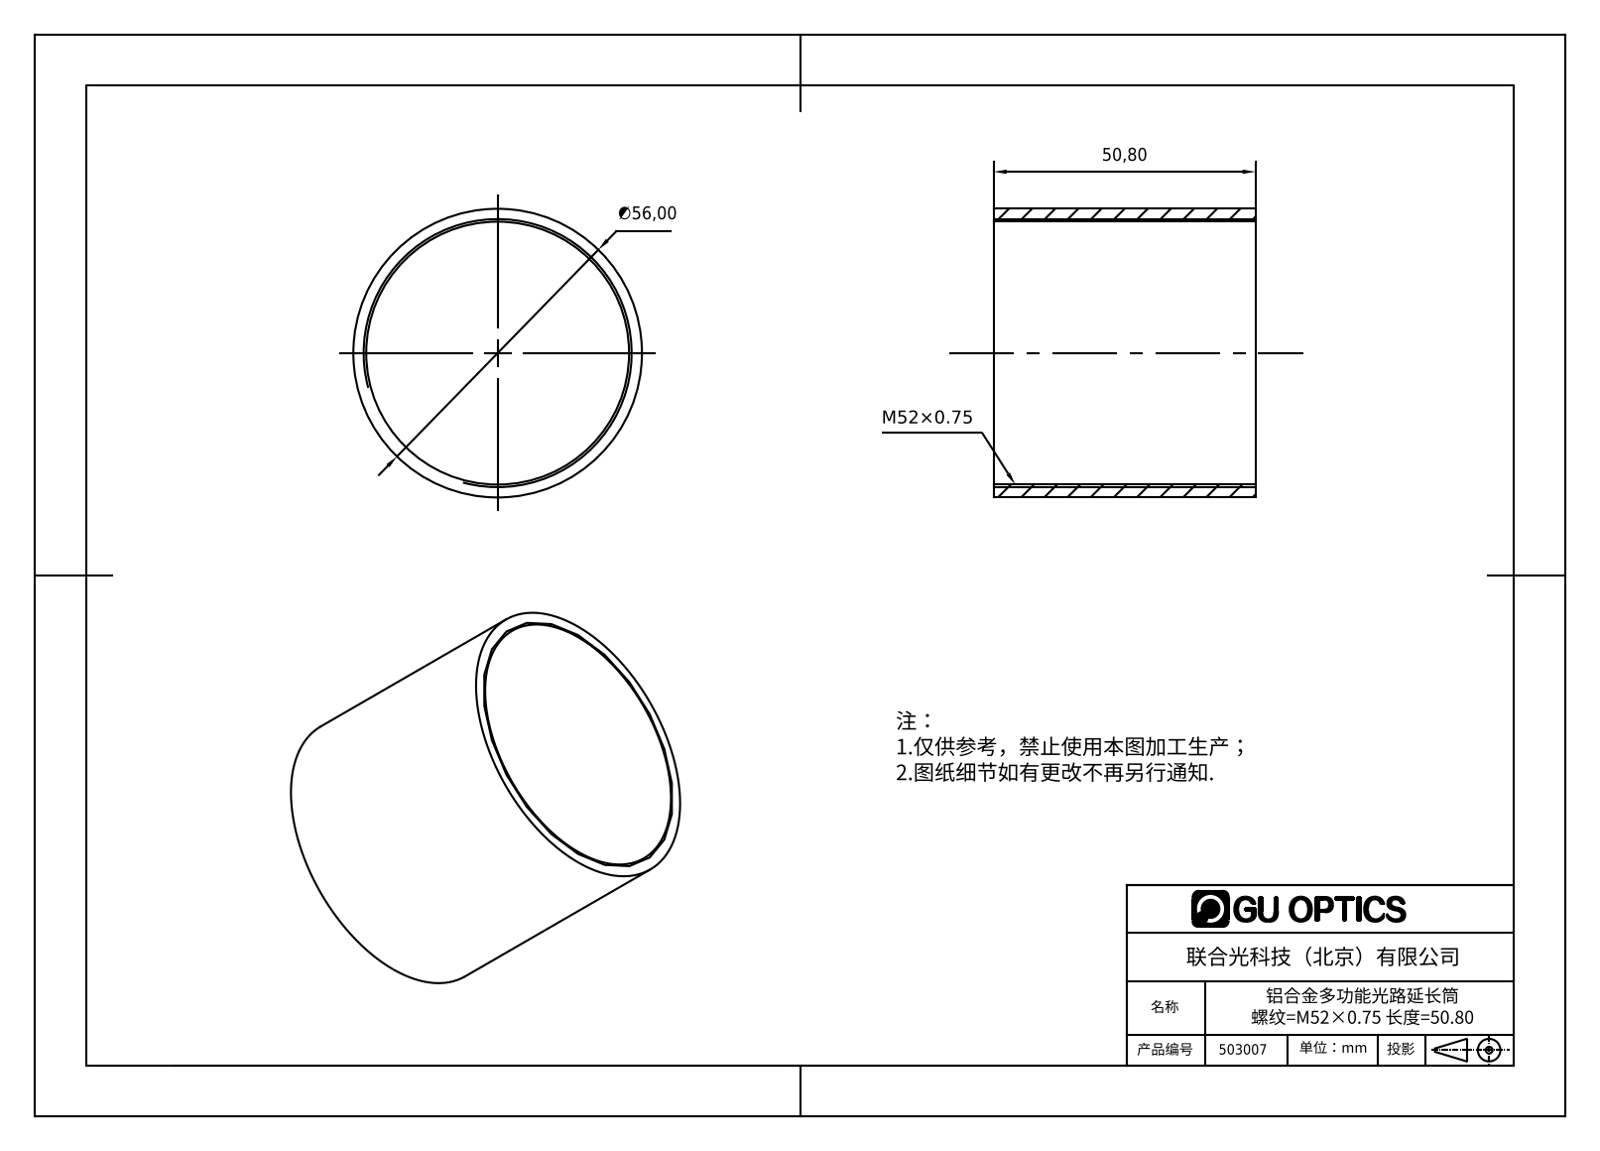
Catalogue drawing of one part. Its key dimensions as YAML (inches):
part_name: "503007"
step_written_by: "SolidWorks 2016 (AUTOMOTIVE_DESIGN)"
units: inches
bodies: {solids: 1, faces: 6, planar: 2, cylindrical: 4, other: 0}
overall_size: [2.205, 2.205, 2]
volume: 1.303
surface_area: 27.77
round_holes:
  - {diameter: 2.008, count: 1}
round_bosses_or_shafts:
  - {diameter: 2.205, count: 1}
face_to_face_distances: [2]
